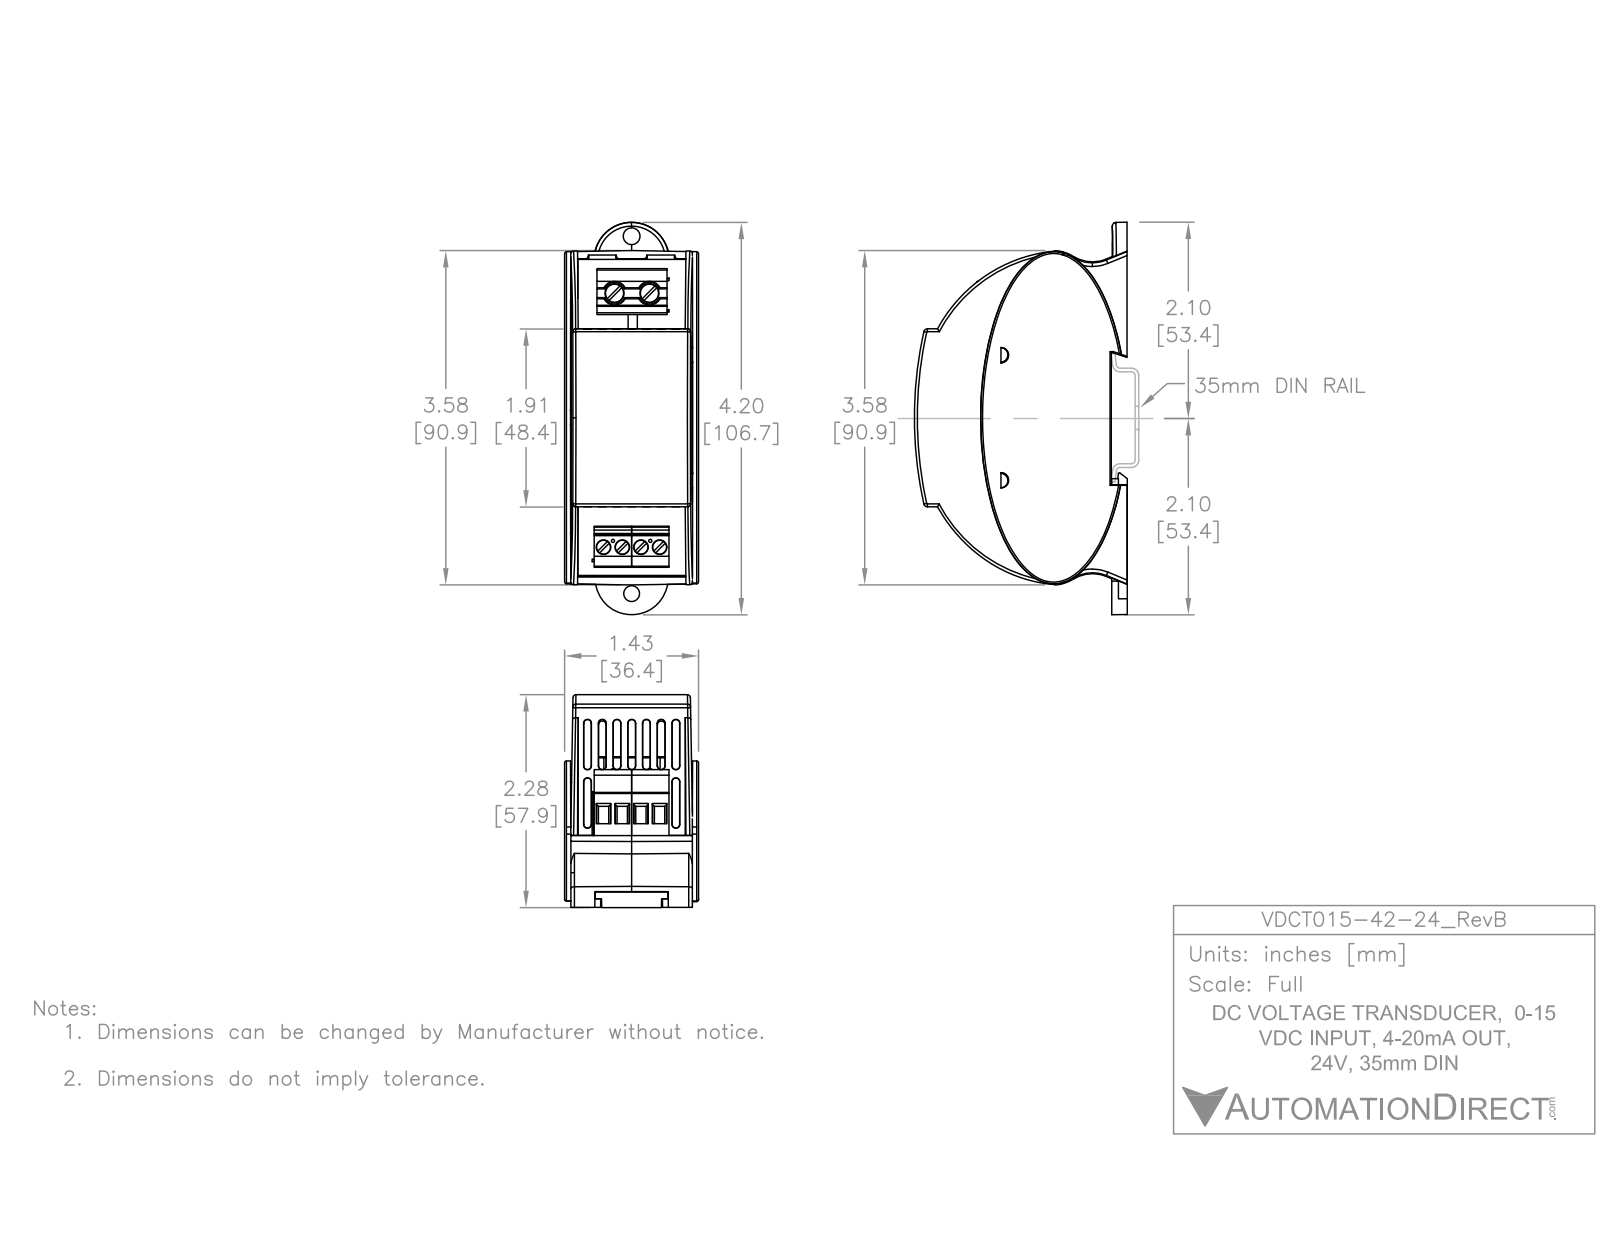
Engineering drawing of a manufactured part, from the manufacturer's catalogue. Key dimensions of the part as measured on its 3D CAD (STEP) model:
Part name (STEP PRODUCT): VDCT015-42-24
STEP written by: SolidWorks 2021 (AUTOMOTIVE_DESIGN)
Units: inches
Bodies: 7 solids, 895 faces (538 planar, 166 cylindrical, 191 other)
Overall size (bounding box): 4.203 × 2.28 × 1.435
Volume: 3.182 in³ · Surface area: 78.38 in²
Round holes (diameter × count): ⌀0.157 ×4, ⌀0.205 ×2
Round bosses / shafts (diameter × count): ⌀0.051 ×6, ⌀0.15 ×4, ⌀0.197 ×2, ⌀0.018 ×2
Partial cylindrical surfaces — rounded edges, fillets, slot ends (radius × count): R0.006 ×20, R0.039 ×12, R0.02 ×11, R0.008 ×8, R0.026 ×8, R0.012 ×4, R0.032 ×4, R0.04 ×4
Main face-to-face distances: 1.435, 0.064, 0.5, 0.435, 0.266, 0.701, 0.765, 1.263, 1.265, 1.129
Hole centre spacings: 0.2, 0.4, 0.375, 0.6, 2.719, 2.719, 2.72, 2.72
